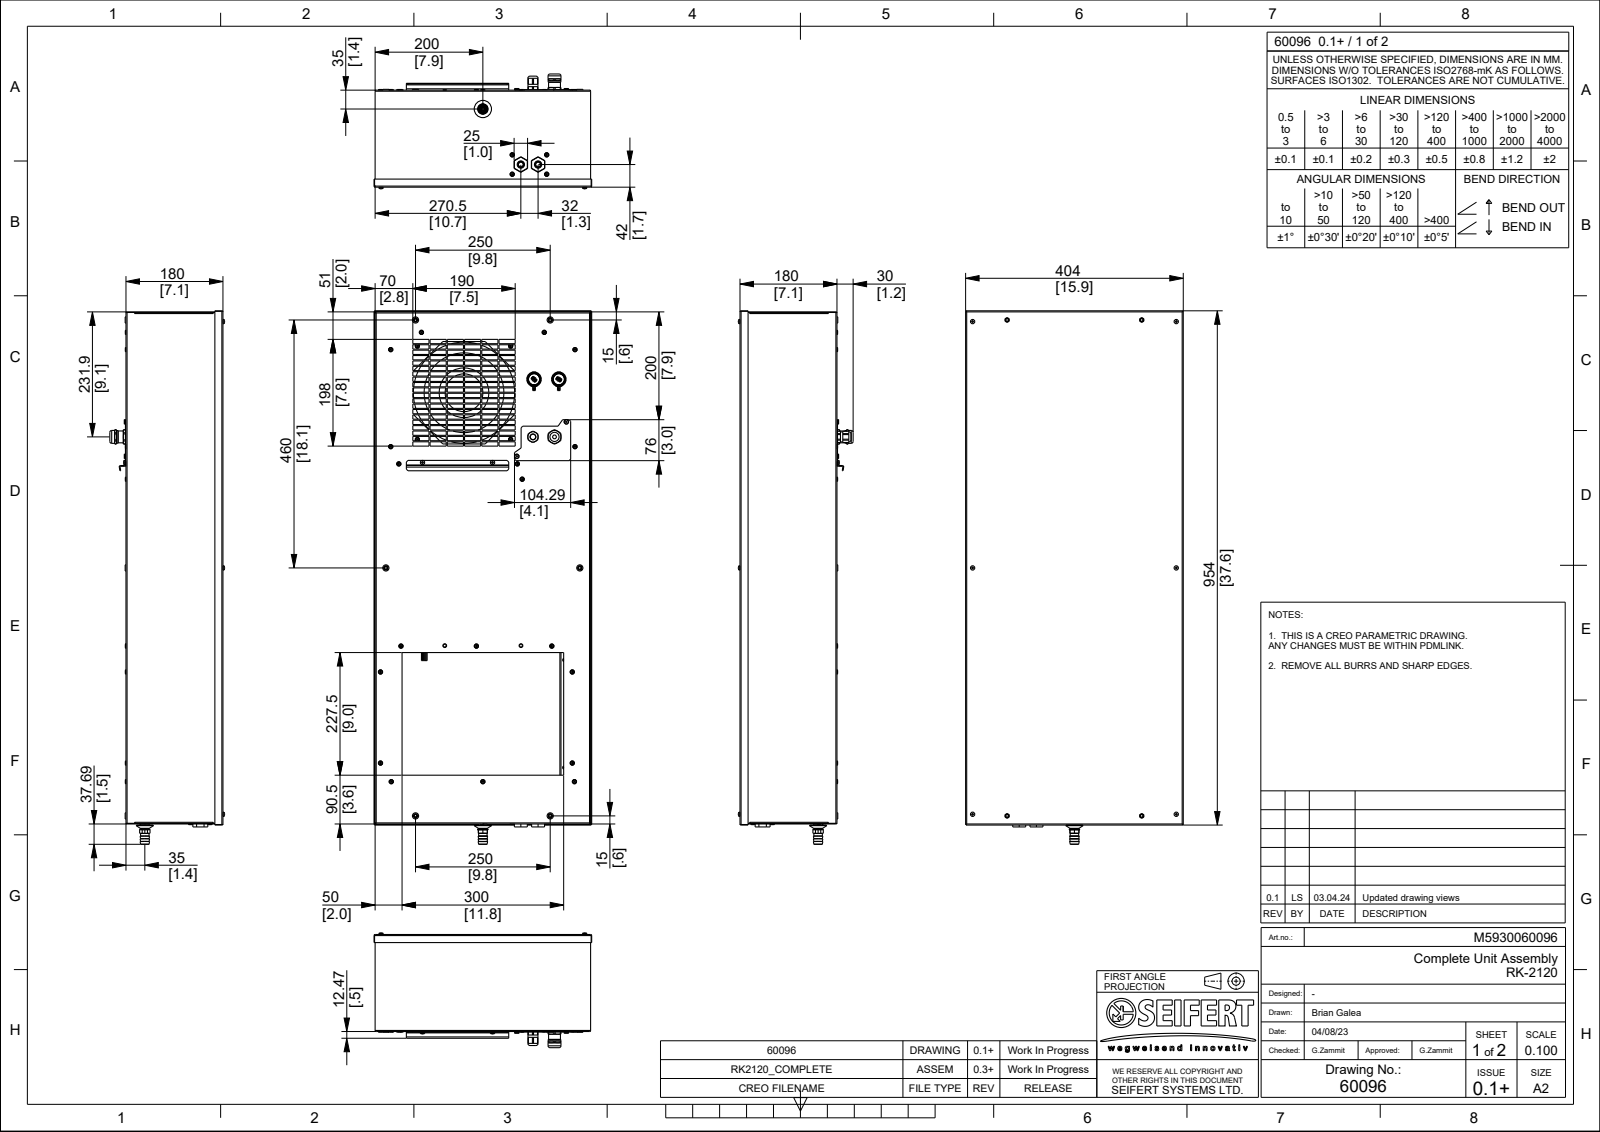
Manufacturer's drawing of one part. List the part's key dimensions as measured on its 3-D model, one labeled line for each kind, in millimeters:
Part name (STEP PRODUCT): 60096
STEP written by: CREO PARAMETRIC BY PTC INC, 2023294 (CONFIG_CONTROL_DESIGN)
Units: millimetres
Bodies: 13 solids, 5729 faces (3033 planar, 1007 cylindrical, 1689 other)
Overall size (bounding box): 1004.44 × 404 × 210
Volume: 1 301 000 mm³ · Surface area: 2 622 000 mm²
Round holes (diameter × count): ⌀4.5 ×25, ⌀7 ×17, ⌀6 ×16, ⌀4 ×6, ⌀5 ×6, ⌀5.5 ×6, ⌀0.8 ×5, ⌀3 ×4, ⌀8 ×4, ⌀2.9 ×2, ⌀3.9 ×2, ⌀9 ×2
Round bosses / shafts (diameter × count): ⌀11.5 ×6, ⌀9 ×6, ⌀24.2 ×3, ⌀17.5 ×2, ⌀16.6 ×2, ⌀14.7 ×2, ⌀8.28 ×2, ⌀4 ×2
Partial cylindrical surfaces — rounded edges, fillets, slot ends (radius × count): R0.5 ×86, R0.3 ×68, R2.5 ×36, R1 ×28, R1.5 ×19, R2 ×18, R4.73 ×16, R0.2 ×14
Main face-to-face distances: 1, 179, 399, 178, 180, 400, 2, 398, 949, 177
Hole centre spacings: 0.84, 24.08, 51.26, 64.07, 314.01, 457, 464.43, 556.95
